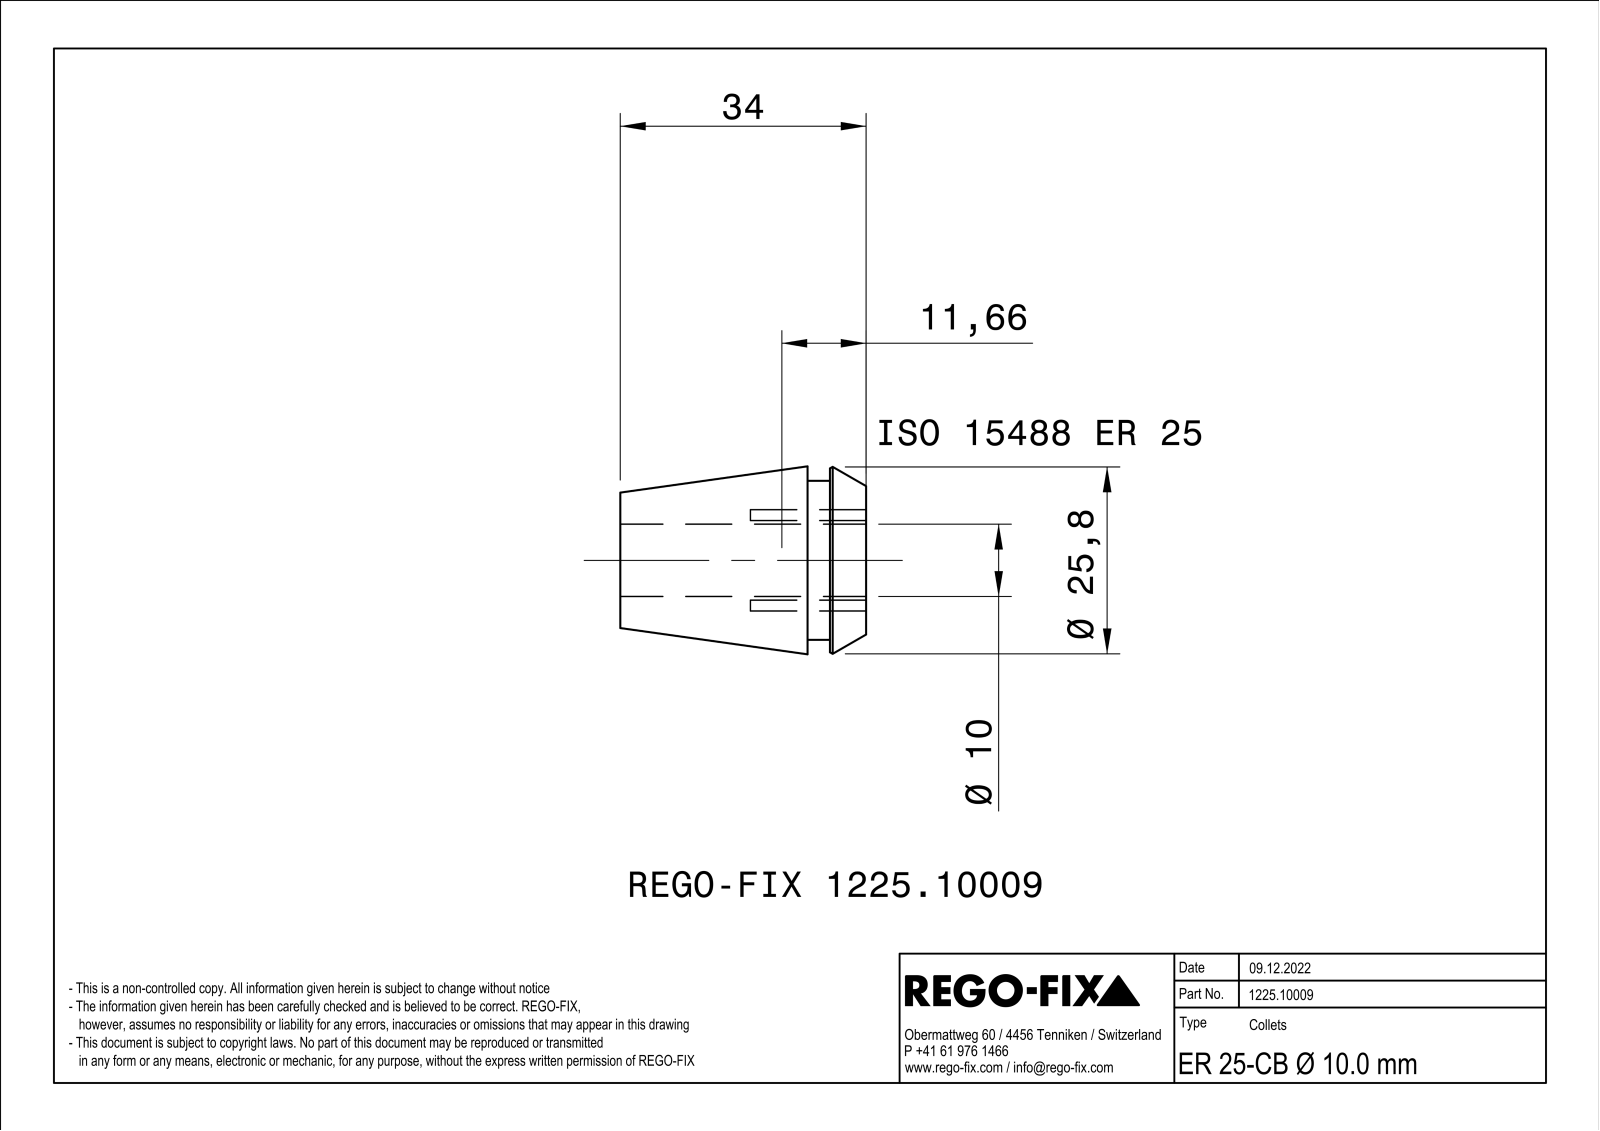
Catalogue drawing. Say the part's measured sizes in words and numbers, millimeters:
The part is named "NOCUT". Its 3-D file was written by "SIEMENS PLM Software Solid Edge ST10 (AUTOMOTIVE_DESIGN)". It is 1 solid with 178 faces: 64 planar, 21 cylindrical and 93 other. Overall it measures 34 by 25.99 by 25.99 millimeters. Its volume is 8 886 cubic millimeters and its surface area 8 679 square millimeters. Round holes: 4 of diameter 1.5, 1 of diameter 10. Round bosses or shafts: 1 of diameter 26, 1 of diameter 22. The main face-to-face distances are 0.8, 34, 5, 29, 8.1, 3.1, 25.9. The hole center spacings are 6.25, 8.83, 12.49.
